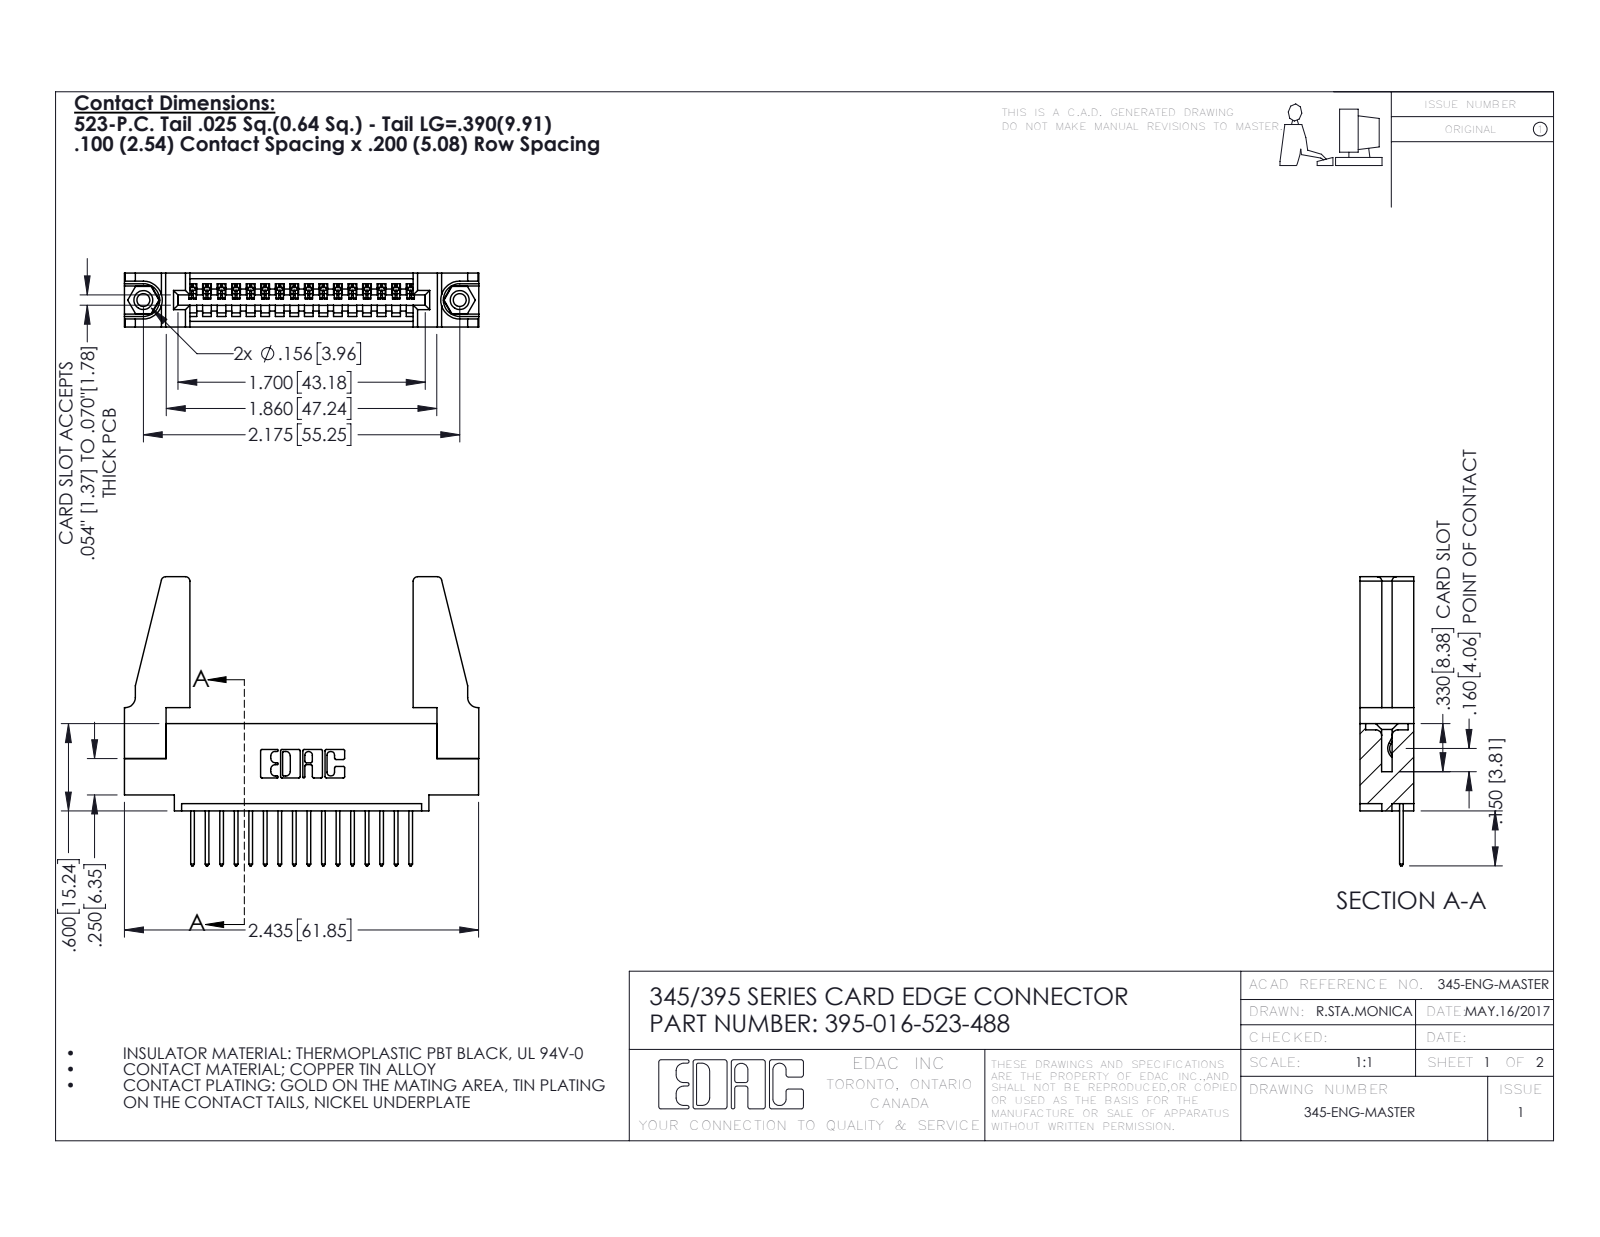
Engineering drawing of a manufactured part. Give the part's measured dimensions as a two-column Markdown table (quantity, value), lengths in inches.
| quantity | value |
| --- | --- |
| part name | 395-016-523-488; 345-250-001_345-250-001-102; 345-220-078_345-220-088; 345-292-001_345-293-123 (+1 more) |
| STEP written by | SolidWorks 2016 (CONFIG_CONTROL_DESIGN) |
| units | inches |
| bodies | 21 solids, 1182 faces (796 planar, 370 cylindrical, 16 other) |
| overall size | 2.436 × 1.987 × 0.37 |
| volume | 0.539 in³ |
| surface area | 15.96 in² |
| round holes (diameter × count) | 0.089 × 2, 0.125 × 2, 0.156 × 2, 0.064 × 1 |
| round bosses / shafts (diameter × count) | 0.155 × 2 |
| partial cylindrical surfaces (radius × count) | 0.006 × 32, 0.01 × 32, 0.01 × 22, 0.03 × 8, 0.007 × 6, 0.031 × 6, 0.026 × 3, 0.031 × 2 |
| main face-to-face distances | 0.37, 0.072, 0.298, 0.2, 0.098, 0.272, 0.025, 0.225, 0.148, 0.15 |
| hole center spacings | 0.27, 1.942, 2.175 |
